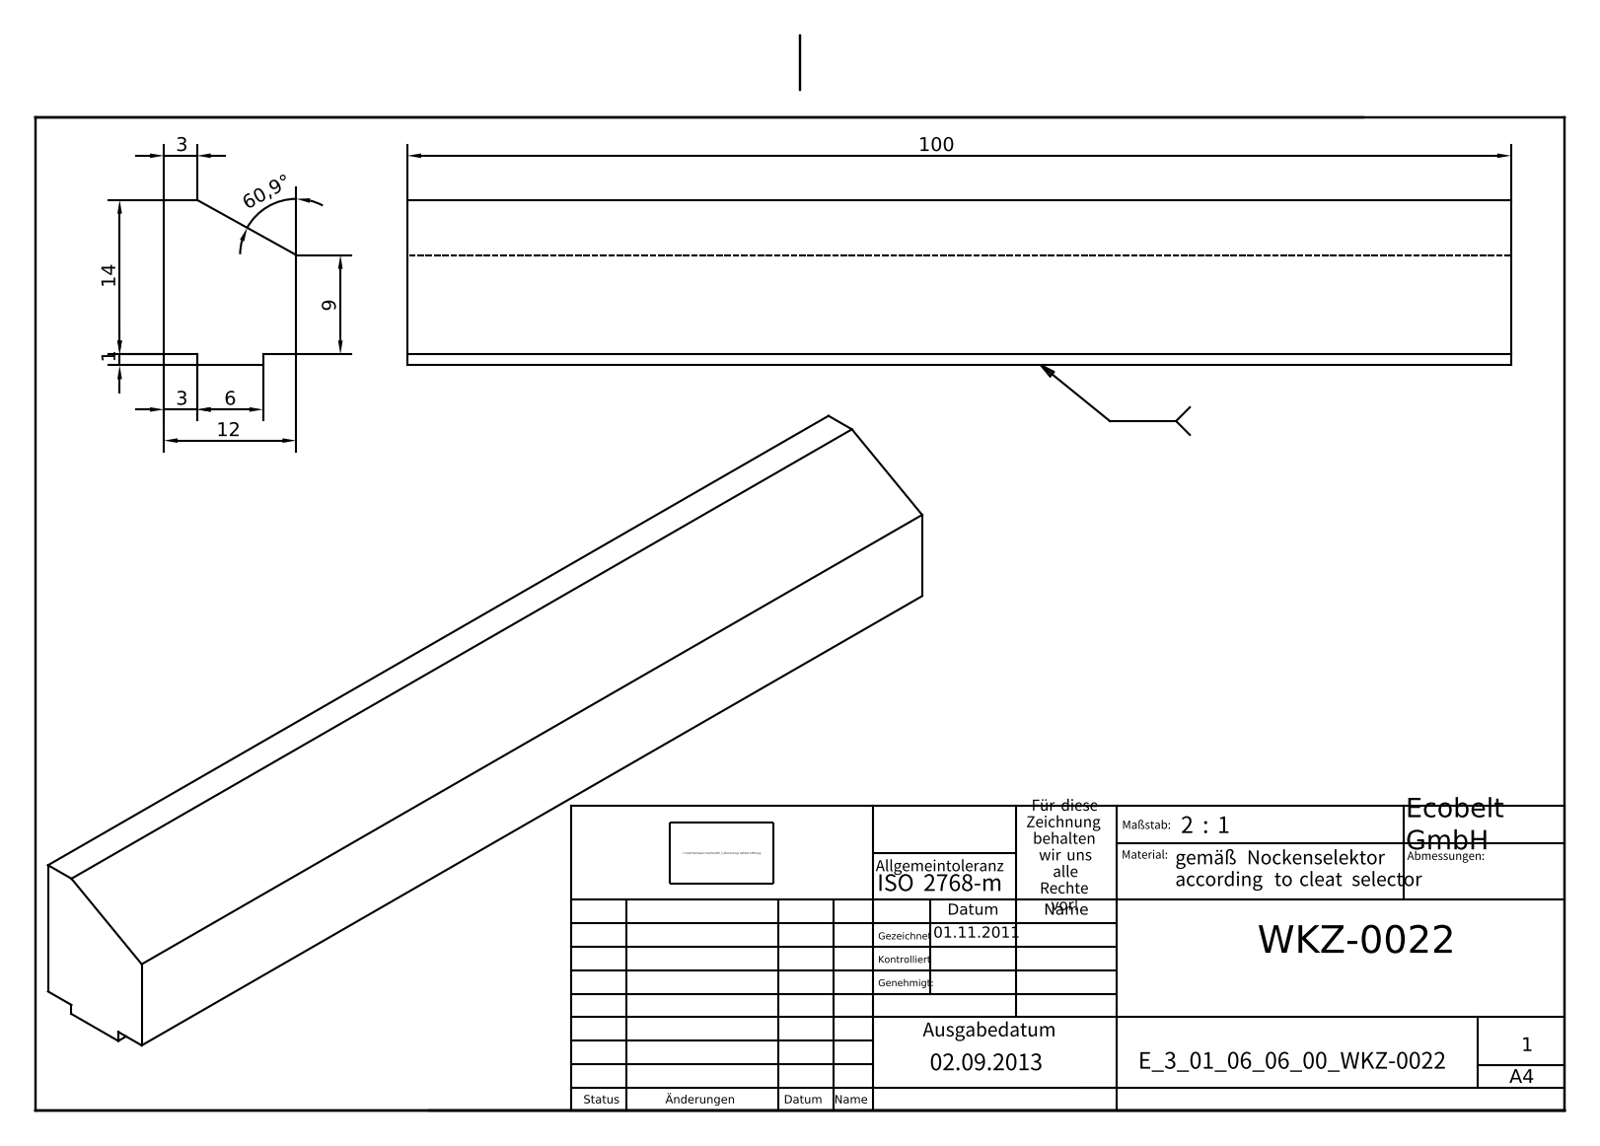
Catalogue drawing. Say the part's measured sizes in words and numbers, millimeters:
The part is named "E_3_01_06_06_00_WKZ-0022". Its 3-D file was written by "Autodesk Inventor 2021 (AUTOMOTIVE_DESIGN)". It is 1 solid with 11 faces: 11 planar, 0 cylindrical and 0 other. Overall it measures 100 by 15 by 12 millimeters. Its volume is 15 150 cubic millimeters and its surface area 5 333 square millimeters. The main face-to-face distances are 12, 1, 15, 14, 3, 9, 100, 6.
